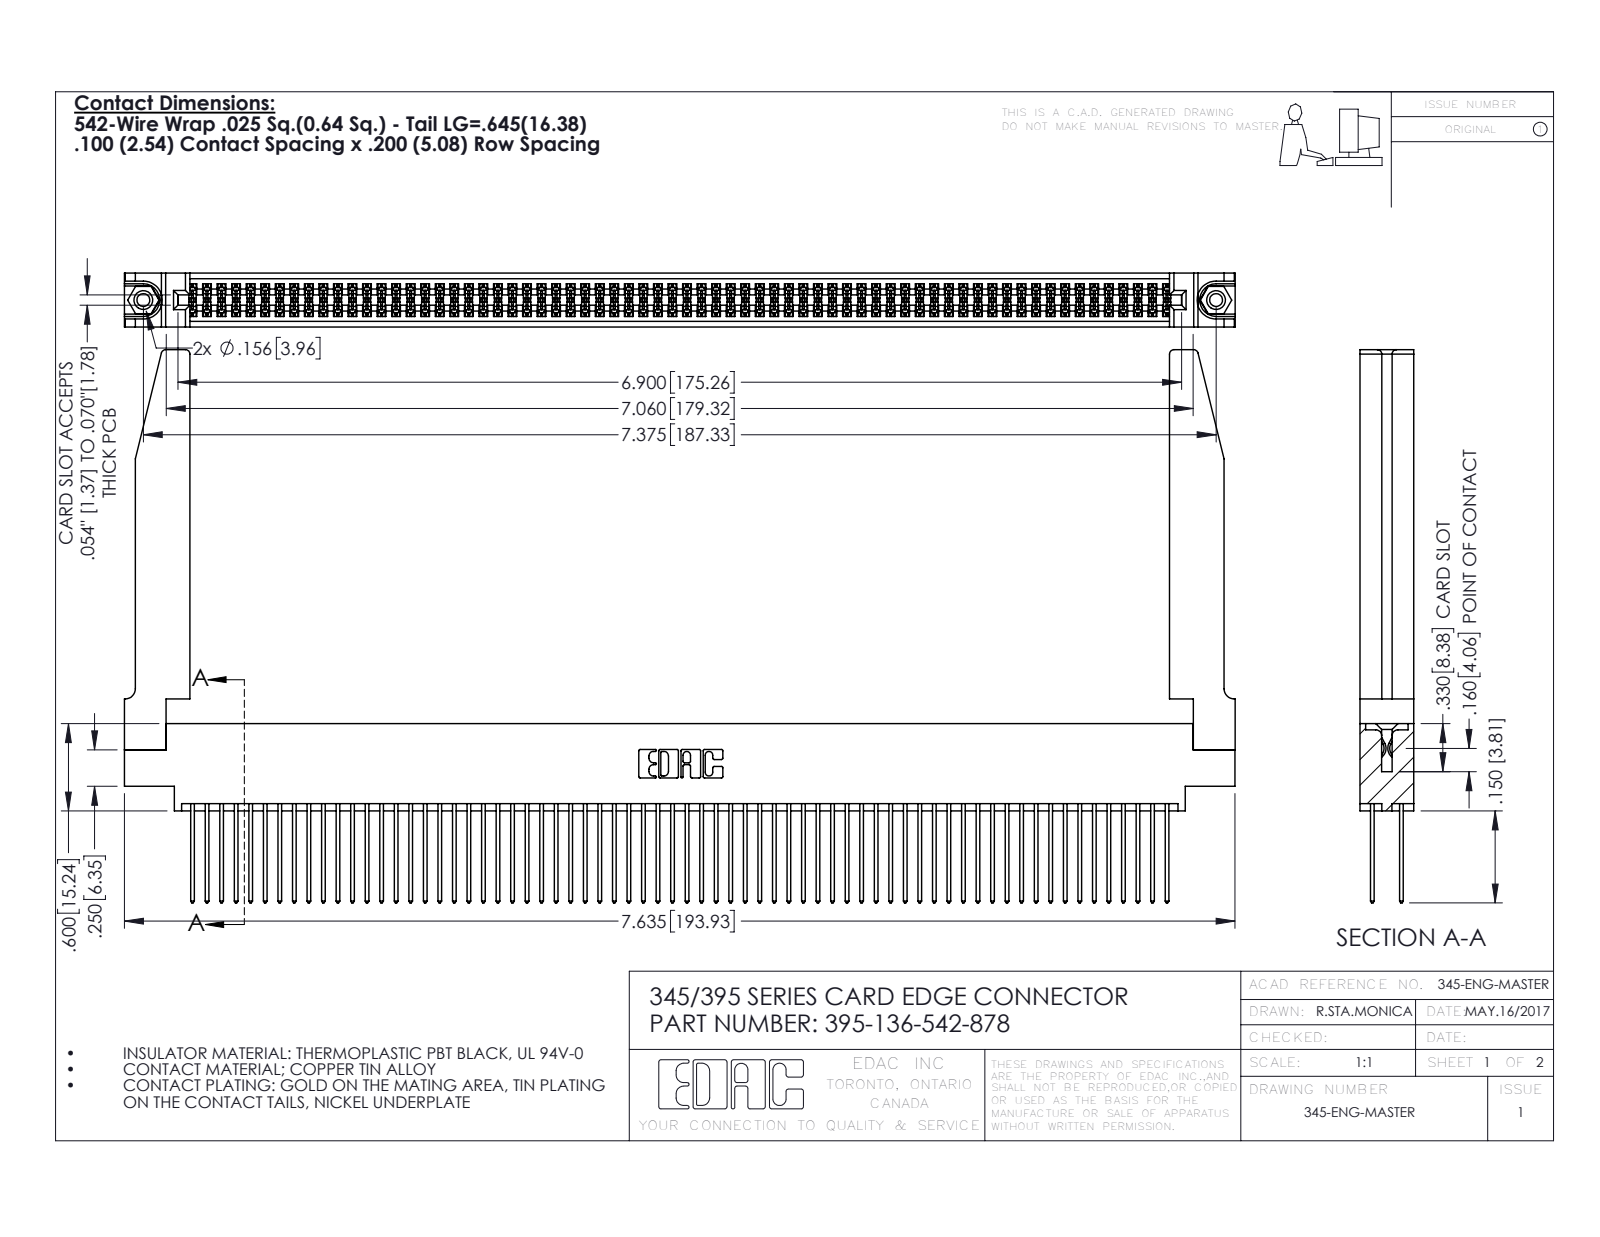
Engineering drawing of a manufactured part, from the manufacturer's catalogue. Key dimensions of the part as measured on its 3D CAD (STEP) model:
Part name (STEP PRODUCT): 345-220-078_345-220-078; 345-292-001_345-293-142; 395-136-542-878; 345-250-001_345-250-001-102 (+1 more)
STEP written by: SolidWorks 2016 (CONFIG_CONTROL_DESIGN)
Units: inches
Bodies: 141 solids, 7164 faces (4714 planar, 2398 cylindrical, 52 other)
Overall size (bounding box): 7.636 × 3.802 × 0.37
Volume: 1.67 in³ · Surface area: 61.11 in²
Round holes (diameter × count): ⌀0.089 ×2, ⌀0.125 ×2, ⌀0.156 ×2, ⌀0.064 ×1
Round bosses / shafts (diameter × count): ⌀0.155 ×2
Partial cylindrical surfaces — rounded edges, fillets, slot ends (radius × count): R0.006 ×204, R0.01 ×136, R0.01 ×22, R0.03 ×8, R0.007 ×6, R0.031 ×6, R0.026 ×3, R0.014 ×2
Main face-to-face distances: 0.072, 0.298, 0.37, 0.098, 0.272, 0.025, 0.2, 0.225, 0.175, 0.149
Hole centre spacings: 0.27, 7.139, 7.375
